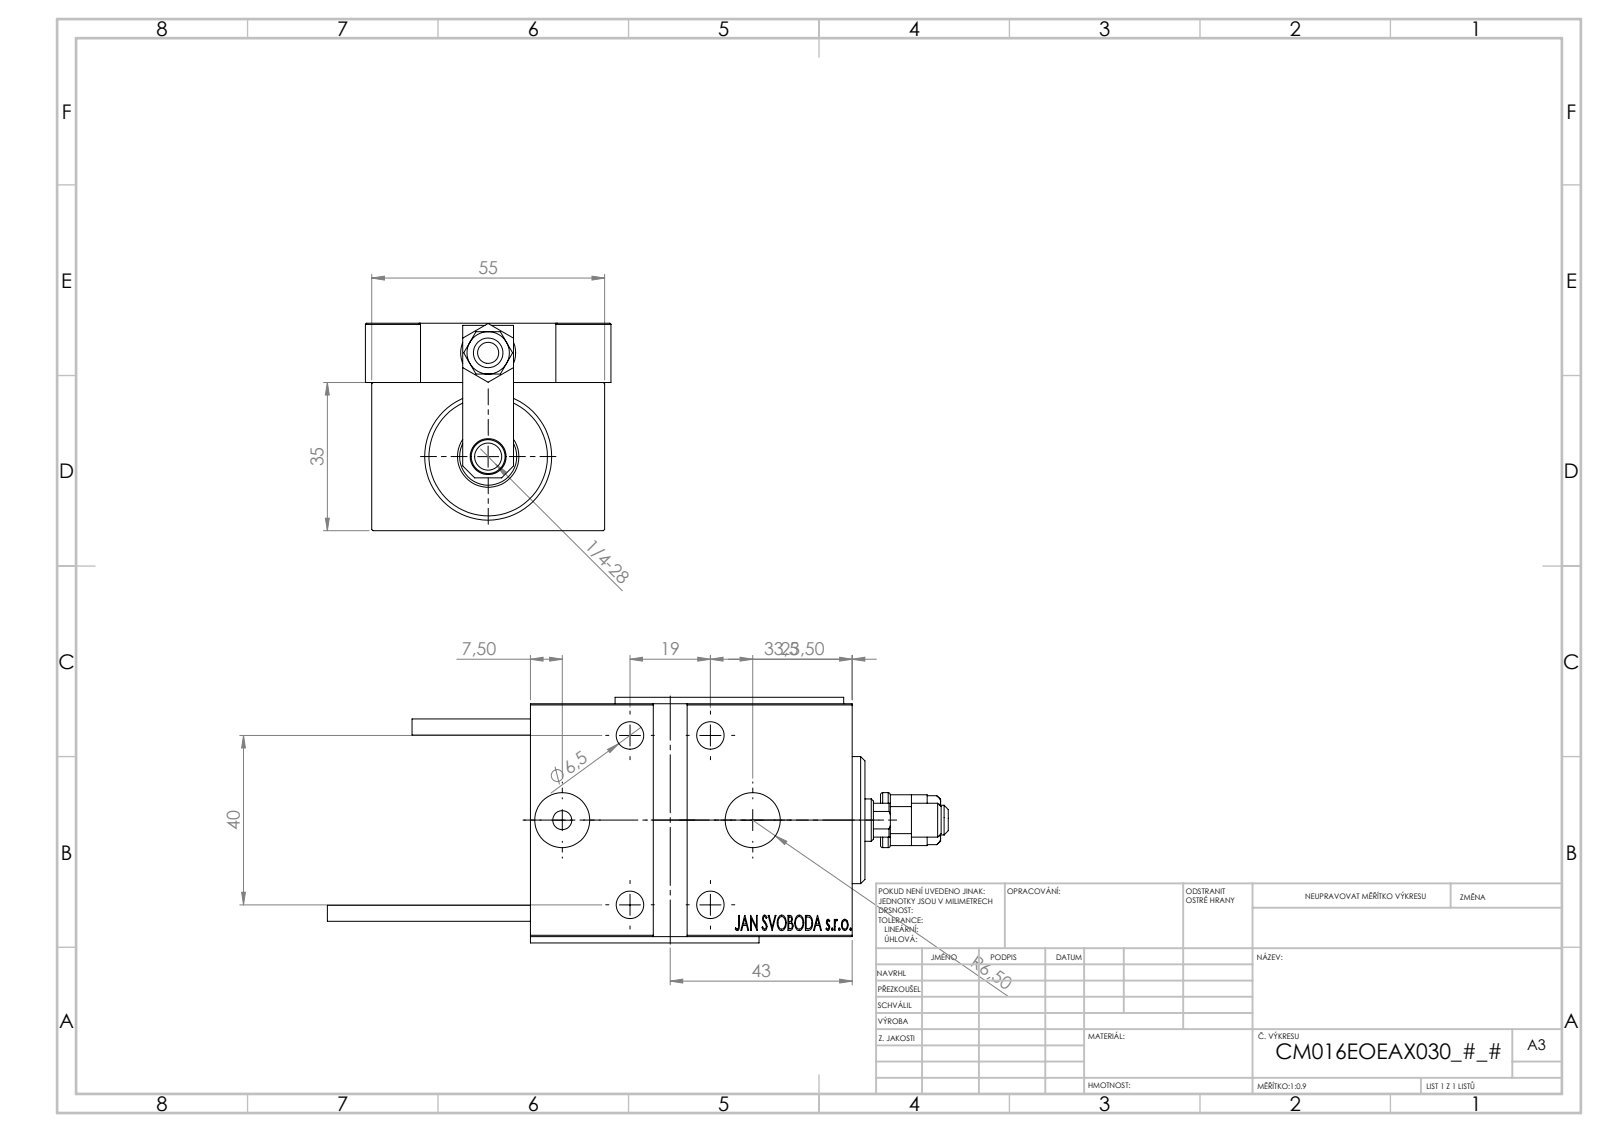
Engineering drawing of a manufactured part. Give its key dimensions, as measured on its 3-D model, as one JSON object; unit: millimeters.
{"part_name": "ZARAZKA; ALLEN BOLT D8; NUT_D10; V450CM_E_Body (+7 more)", "step_written_by": "SolidWorks 2019 (CONFIG_CONTROL_DESIGN)", "units": "millimeters", "bodies": {"solids": 25, "faces": 1303, "planar": 574, "cylindrical": 182, "other": 547}, "overall_size": [146.7, 58, 49], "volume_mm3": 181485, "surface_area_mm2": 54007, "round_holes": [[8, 5], [3.2, 4], [4, 4], [6.5, 4], [10.5, 4], [5, 2], [13, 2], [4.5, 1], [7, 1], [8.5, 1], [10, 1], [13.5, 1]], "round_bosses_or_shafts": [[5, 2], [3.8, 2], [30, 1], [18, 1], [13, 1], [11, 1], [8, 1], [6, 1]], "partial_cylinders_radius": [[0.3, 30], [3, 2], [4.5, 1]], "face_to_face_distances": [35, 14, 55, 49, 10, 5, 45, 3, 20, 1.5], "hole_center_spacings": [10.31, 11.37, 12.42, 19, 19.29, 20, 21.03, 22.36]}
